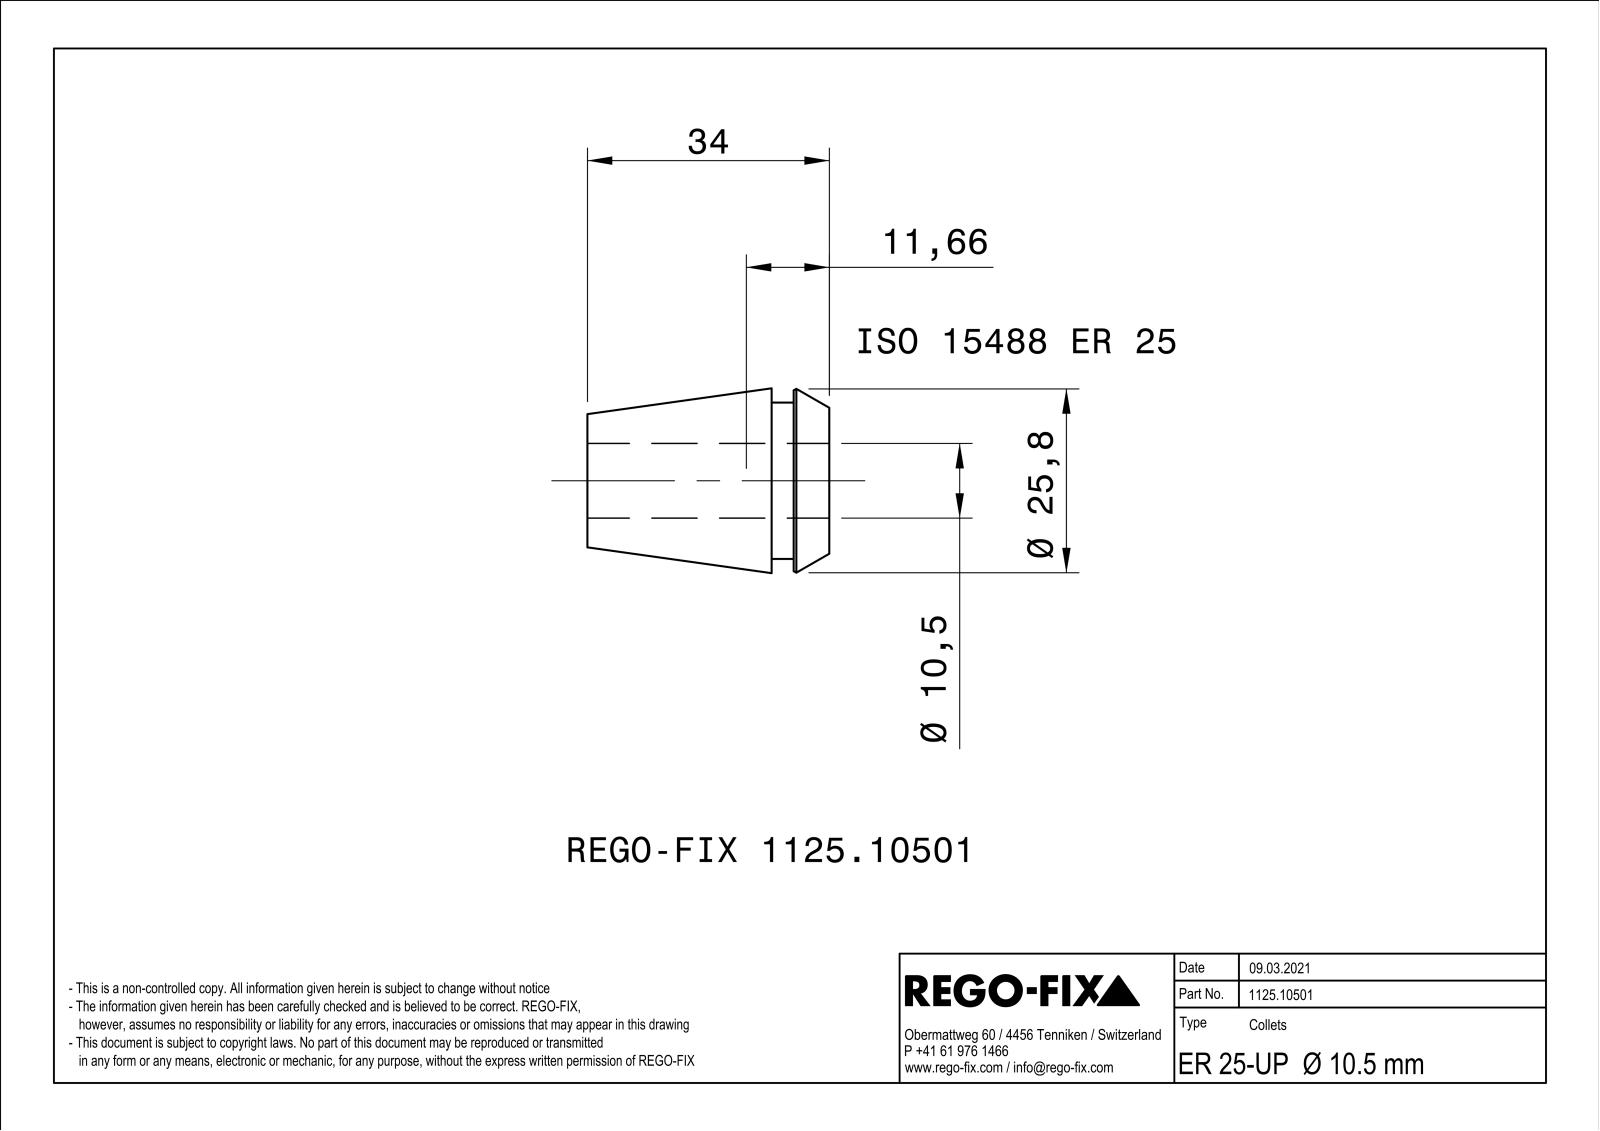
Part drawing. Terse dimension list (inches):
name: NOCUT
written by: SIEMENS PLM Software Solid Edge ST10 (AUTOMOTIVE_DESIGN)
unit: in
bodies: 1 solid, 177 faces (72 planar, 25 cylindrical, 80 other)
size: 1.339 × 1.023 × 1.023
volume: 0.51 in³; area: 14.29 in²
holes: 1× ⌀0.413
bosses: 1× ⌀0.866
rounds: 8× R0.016
face distances: 0.031, 1.339, 0.319, 1.02, 0.197, 0.122, 1.142
